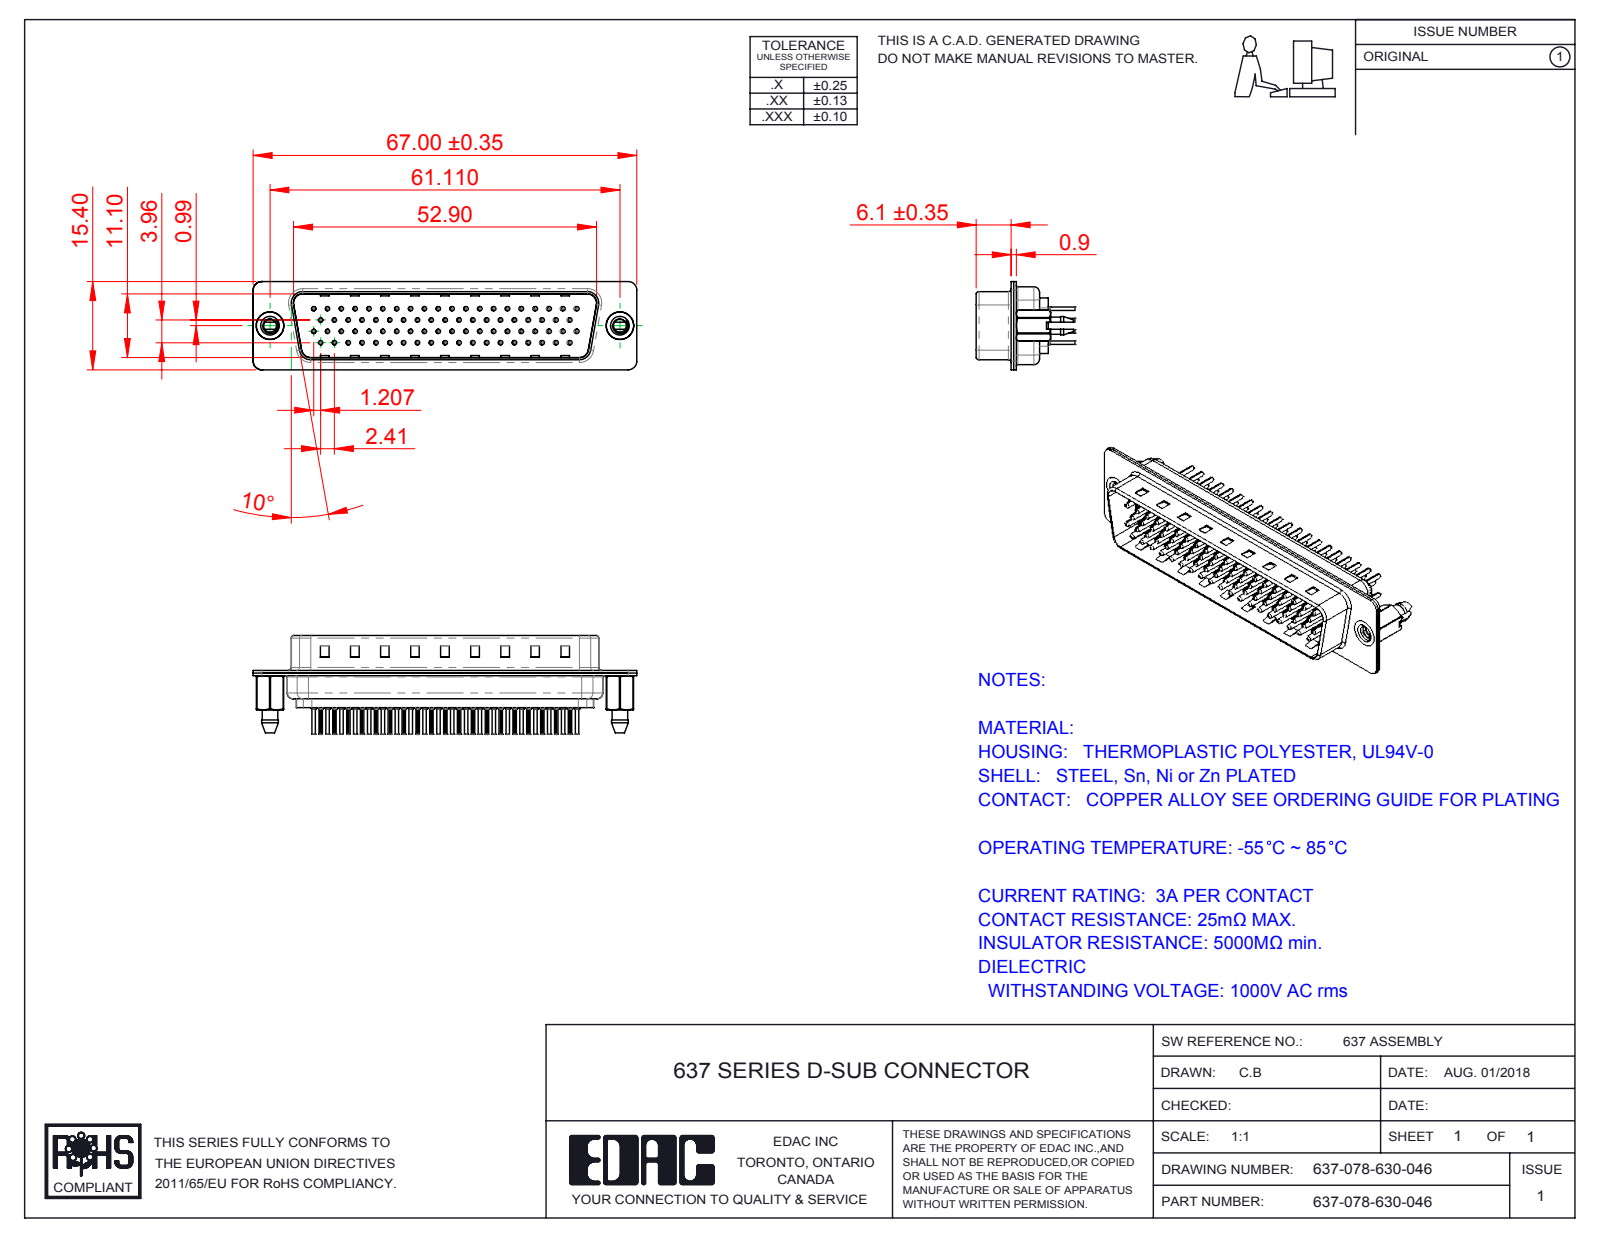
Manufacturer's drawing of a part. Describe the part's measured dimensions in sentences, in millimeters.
The part is named "637 Contact Row 2_30; 637-078-630-046; 637 Contact Row 78_30; 637 Housing_78 Contacts (+5 more)". Its 3-D file was written by "SolidWorks 2016 (CONFIG_CONTROL_DESIGN)". It is 83 solids with 8286 faces: 2107 planar, 3059 cylindrical and 3120 other. Overall it measures 67 by 17.25 by 15.4 millimeters. Its volume is 4 448 cubic millimeters and its surface area 16 150 square millimeters. Round holes: 150 of diameter 1.6, 78 of diameter 0.2, 78 of diameter 0.35, 78 of diameter 1.1, 72 of diameter 0.75, 72 of diameter 2, 3 of diameter 4, 2 of diameter 2.26, 2 of diameter 4.8. Round bosses or shafts: 78 of diameter 2, 78 of diameter 1.5, 78 of diameter 0.75, 78 of diameter 0.6, 2 of diameter 4.9, 1 of diameter 4.8. Partial cylindrical surfaces (rounded edges, fillets, slot ends): 156 of radius 0.1, 18 of radius 1.5, 12 of radius 2, 8 of radius 0.5, 6 of radius 1.6, 4 of radius 0.25, 4 of radius 0.55, 4 of radius 0.7. The main face-to-face distances are 0.45, 0.4, 1.5, 1.95, 11.9, 11.5, 0.7, 11.1, 0.9, 0.8. The hole center spacings are 2.41, 7.24, 6.06, 9.65, 6.96, 8.46, 14.54, 16.89.
